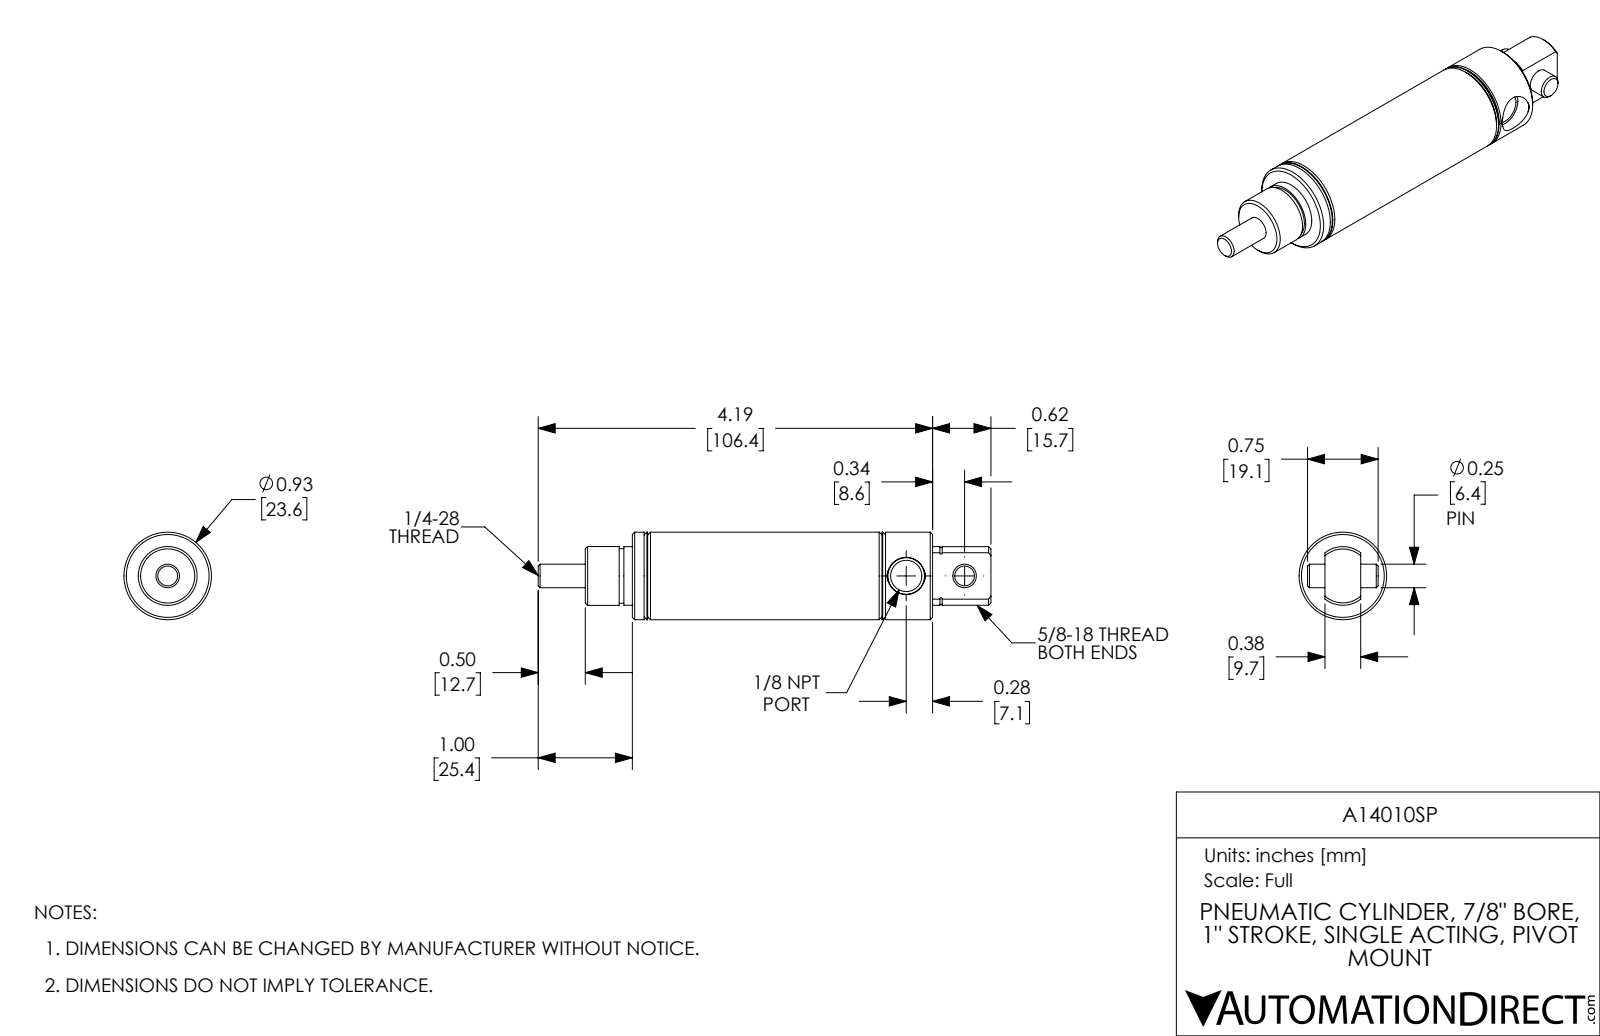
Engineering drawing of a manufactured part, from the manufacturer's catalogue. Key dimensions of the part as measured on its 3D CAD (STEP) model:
Part name (STEP PRODUCT): A14010SP-MainBody; A14010SP; A14010SP-Pin; A14010SP-Rod
STEP written by: SolidWorks 2017 (AUTOMOTIVE_DESIGN)
Units: inches
Bodies: 3 solids, 87 faces (20 planar, 34 cylindrical, 33 other)
Overall size (bounding box): 4.81 × 0.93 × 0.93
Volume: 1.904 in³ · Surface area: 25.19 in²
Round holes (diameter × count): ⌀0.25 ×2, ⌀0.332 ×1, ⌀0.875 ×1
Round bosses / shafts (diameter × count): ⌀0.93 ×1, ⌀0.625 ×1, ⌀0.623 ×1, ⌀0.58 ×1
Main face-to-face distances: 0.5, 1, 1.5, 2.157, 1.033, 3.19, 1.533, 2.533, 1.657, 0.657
Hole centre spacings: 0.62
